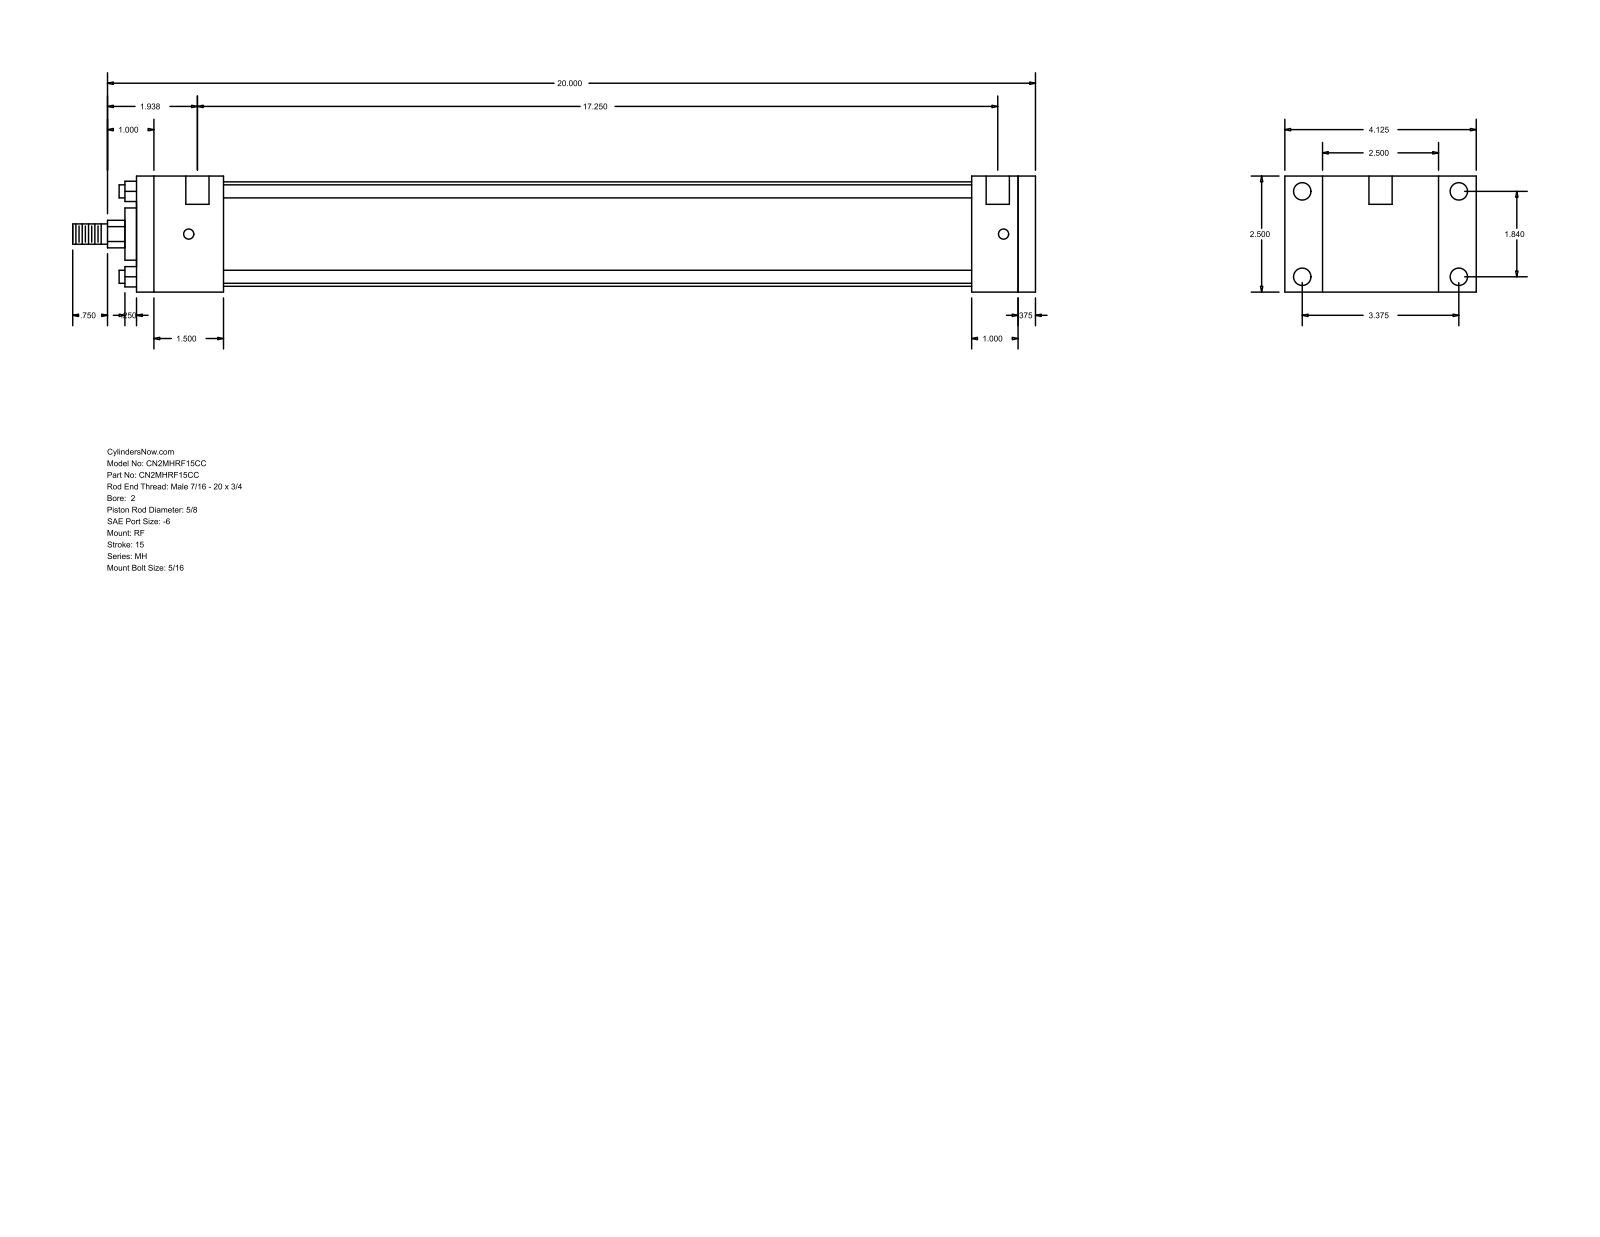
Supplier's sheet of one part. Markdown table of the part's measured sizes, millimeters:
| quantity | value |
| --- | --- |
| part name | MH_RF__0200_0.625 |
| STEP written by | GSSL Pune (CONFIG_CONTROL_DESIGN) |
| units | millimeters |
| bodies | 0 solids, 92 faces (64 planar, 28 cylindrical, 0 other) |
| overall size | 527.05 × 104.78 × 63.5 |
| round holes (diameter × count) | 5.56 × 4, 9.53 × 4, 12.7 × 2 |
| round bosses / shafts (diameter × count) | 7.14 × 4, 57.15 × 1, 28.57 × 1, 15.88 × 1, 11.11 × 1 |
| partial cylindrical surfaces (radius × count) | 7.54 × 1 |
| main face-to-face distances | 63.5, 492.12, 482.6, 9.52, 34.93, 47.62, 457.19, 409.57, 434.98, 444.5 |
| hole center spacings | 46.74, 85.72, 97.63, 446.09, 3.18, 4.76, 438.15, 441.33 |
